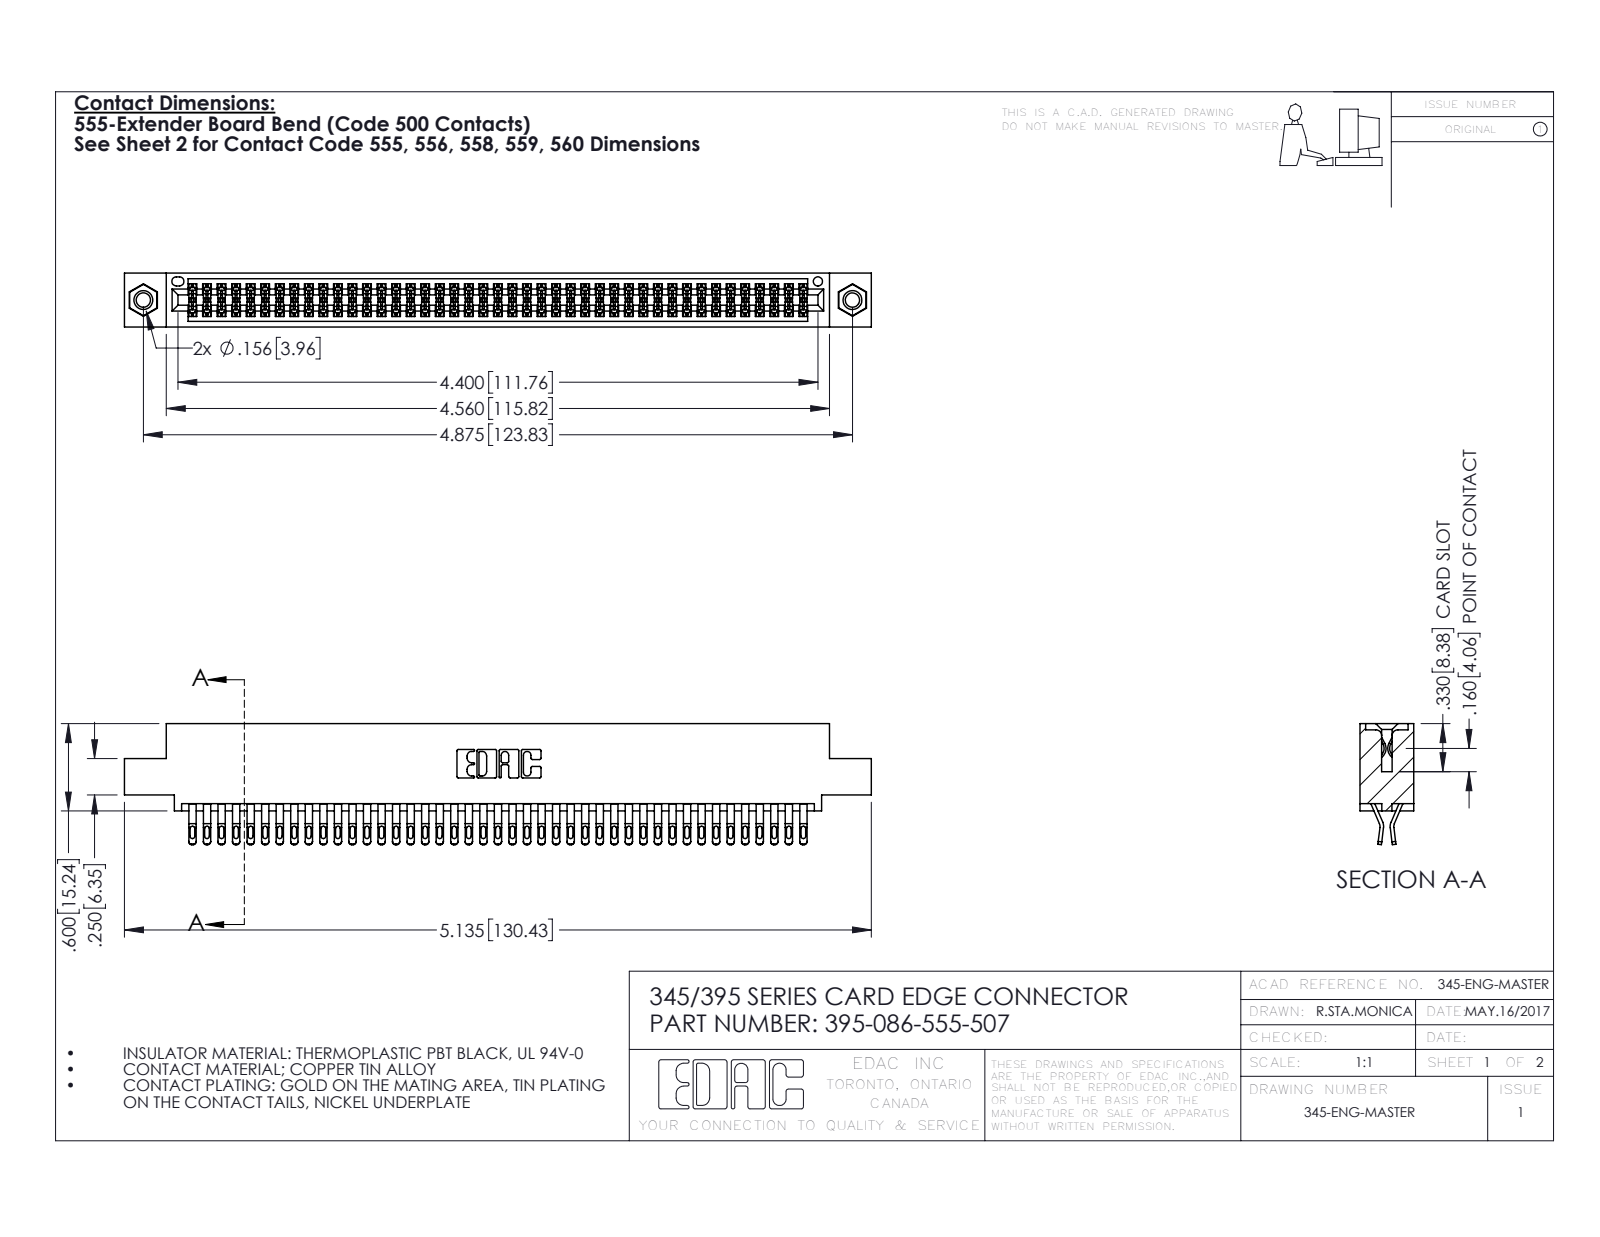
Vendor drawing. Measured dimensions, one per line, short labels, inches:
name: 345 Part_0.110 Offset - 0.156 Dia-TI; 345-250-001_345-250-005-103; 395-086-555-507; 345-292-001_555 Tail
written by: SolidWorks 2016 (CONFIG_CONTROL_DESIGN)
unit: in
bodies: 89 solids, 5006 faces (2782 planar, 2208 cylindrical, 16 other)
size: 5.135 × 0.832 × 0.37
volume: 0.784 in³; area: 30.98 in²
holes: 2× ⌀0.098, 2× ⌀0.125, 2× ⌀0.156, 1× ⌀0.064
bosses: 2× ⌀0.155
rounds: 215× R0.016, 172× R0.02, 129× R0.006, 22× R0.01, 6× R0.007, 6× R0.031, 3× R0.026, 2× R0.01
face distances: 0.072, 0.298, 0.025, 0.37, 0.2, 0.098, 0.272, 0.225, 0.175, 0.149
hole spacings: 0.27, 4.639, 4.875
